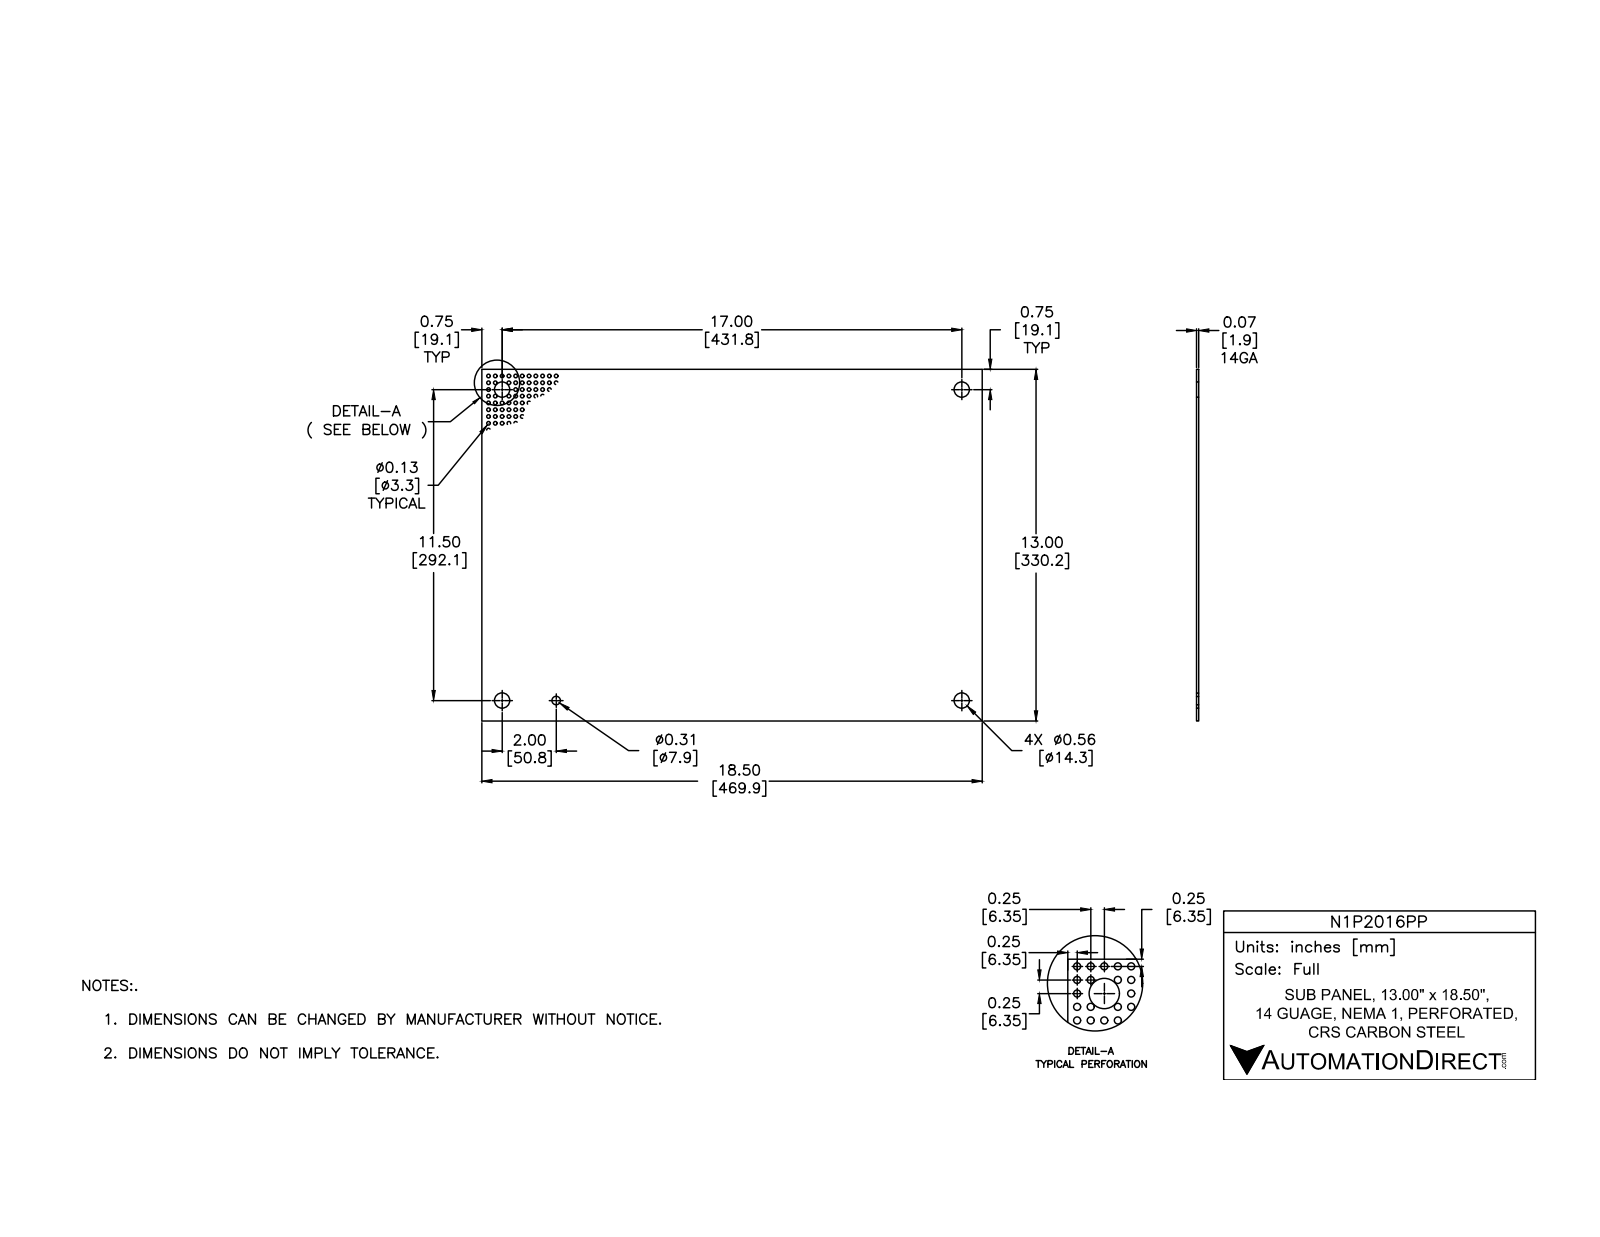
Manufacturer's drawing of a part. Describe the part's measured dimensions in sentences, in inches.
The part is named "N1P_PP-LARGE". Its 3-D file was written by "Autodesk Inventor 2012 (AUTOMOTIVE_DESIGN)". It is 1 solid with 11 faces: 6 planar, 5 cylindrical and 0 other. Overall it measures 18.5 by 13 by 0.074 inches. Its volume is 17.72 cubic inches and its surface area 484.1 square inches. Round holes: 4 of diameter 0.563, 1 of diameter 0.312. The main face-to-face distances are 0.074, 13, 18.5. The hole center spacings are 11.5, 17, 20.524, 2, 11.672, 15, 18.901.
